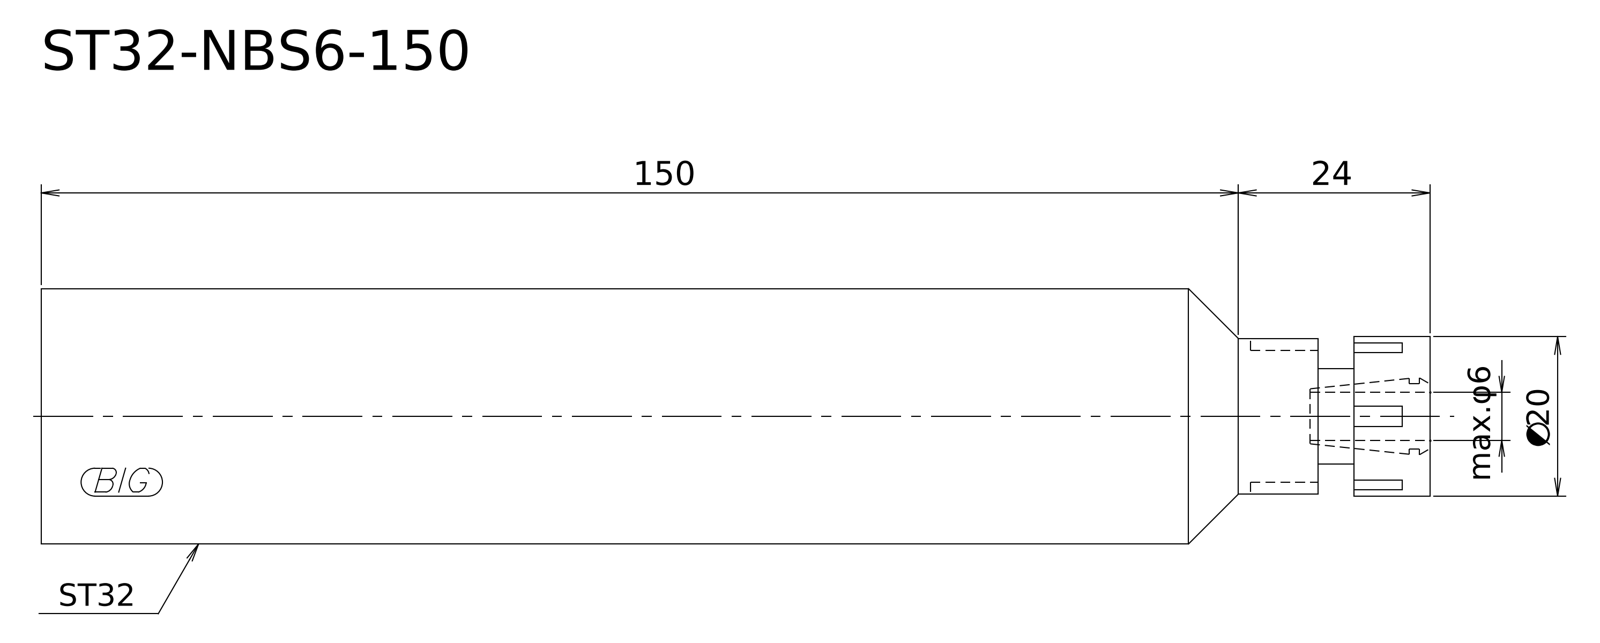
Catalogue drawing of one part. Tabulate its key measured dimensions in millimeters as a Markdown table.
| quantity | value |
| --- | --- |
| STEP written by | Kubotek KeyCreator V8.5.1 (14335) (CONFIG_CONTROL_DESIGN) |
| units | millimeters |
| bodies | 1 solid, 9 faces (4 planar, 4 cylindrical, 1 other) |
| overall size | 174 × 32 × 32 |
| volume | 125 409 mm³ |
| surface area | 18 051 mm² |
| round bosses / shafts (diameter × count) | 32 × 1, 20 × 1, 19.5 × 1, 12 × 1 |
| main face-to-face distances | 174, 9.5, 164.5, 14, 4.5, 160 |
